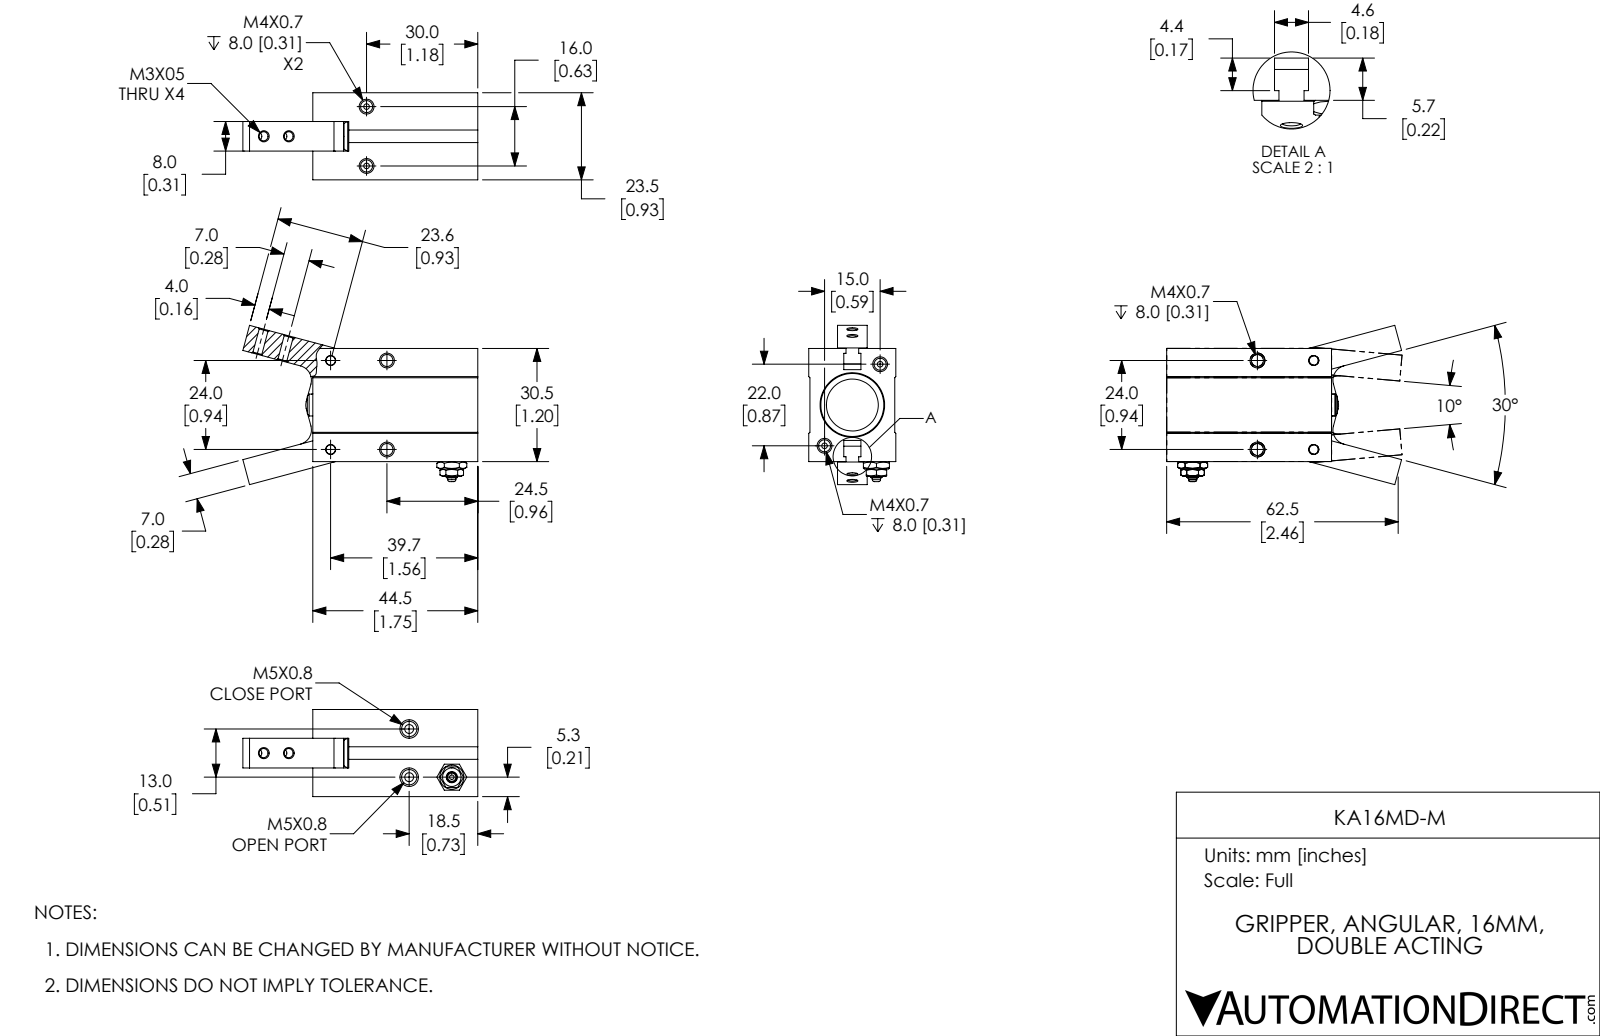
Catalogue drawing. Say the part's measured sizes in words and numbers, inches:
The part is named "KA16MD-M; KA16MD-M-4; KA16MD-M-3; KA16MD-M-2 (+1 more)". Its 3-D file was written by "SolidWorks 2017 (AUTOMOTIVE_DESIGN)". It is 4 solids with 273 faces: 105 planar, 90 cylindrical and 78 other. Overall it measures 2.496 by 1.692 by 0.925 inches. Its volume is 1.632 cubic inches and its surface area 22.5 square inches. Round holes: 6 of diameter 0.128, 4 of diameter 0.097, 2 of diameter 0.098, 2 of diameter 0.163, 2 of diameter 0.165, 1 of diameter 0.083, 1 of diameter 0.315, 1 of diameter 0.551, 1 of diameter 0.63, 1 of diameter 0.669, 1 of diameter 0.709. Round bosses or shafts: 2 of diameter 0.276, 1 of diameter 0.626, 1 of diameter 0.118, 1 of diameter 0.087. Partial cylindrical surfaces (rounded edges, fillets, slot ends): 2 of radius 0.138, 2 of radius 0.157. The main face-to-face distances are 0.913, 0.305, 0.62, 0.293, 0.608, 1.201, 0.067, 0.925, 0.902, 0.091. The hole center spacings are 0.276, 0.457, 0.489, 0.524, 0.598, 0.729, 0.865, 0.945.
